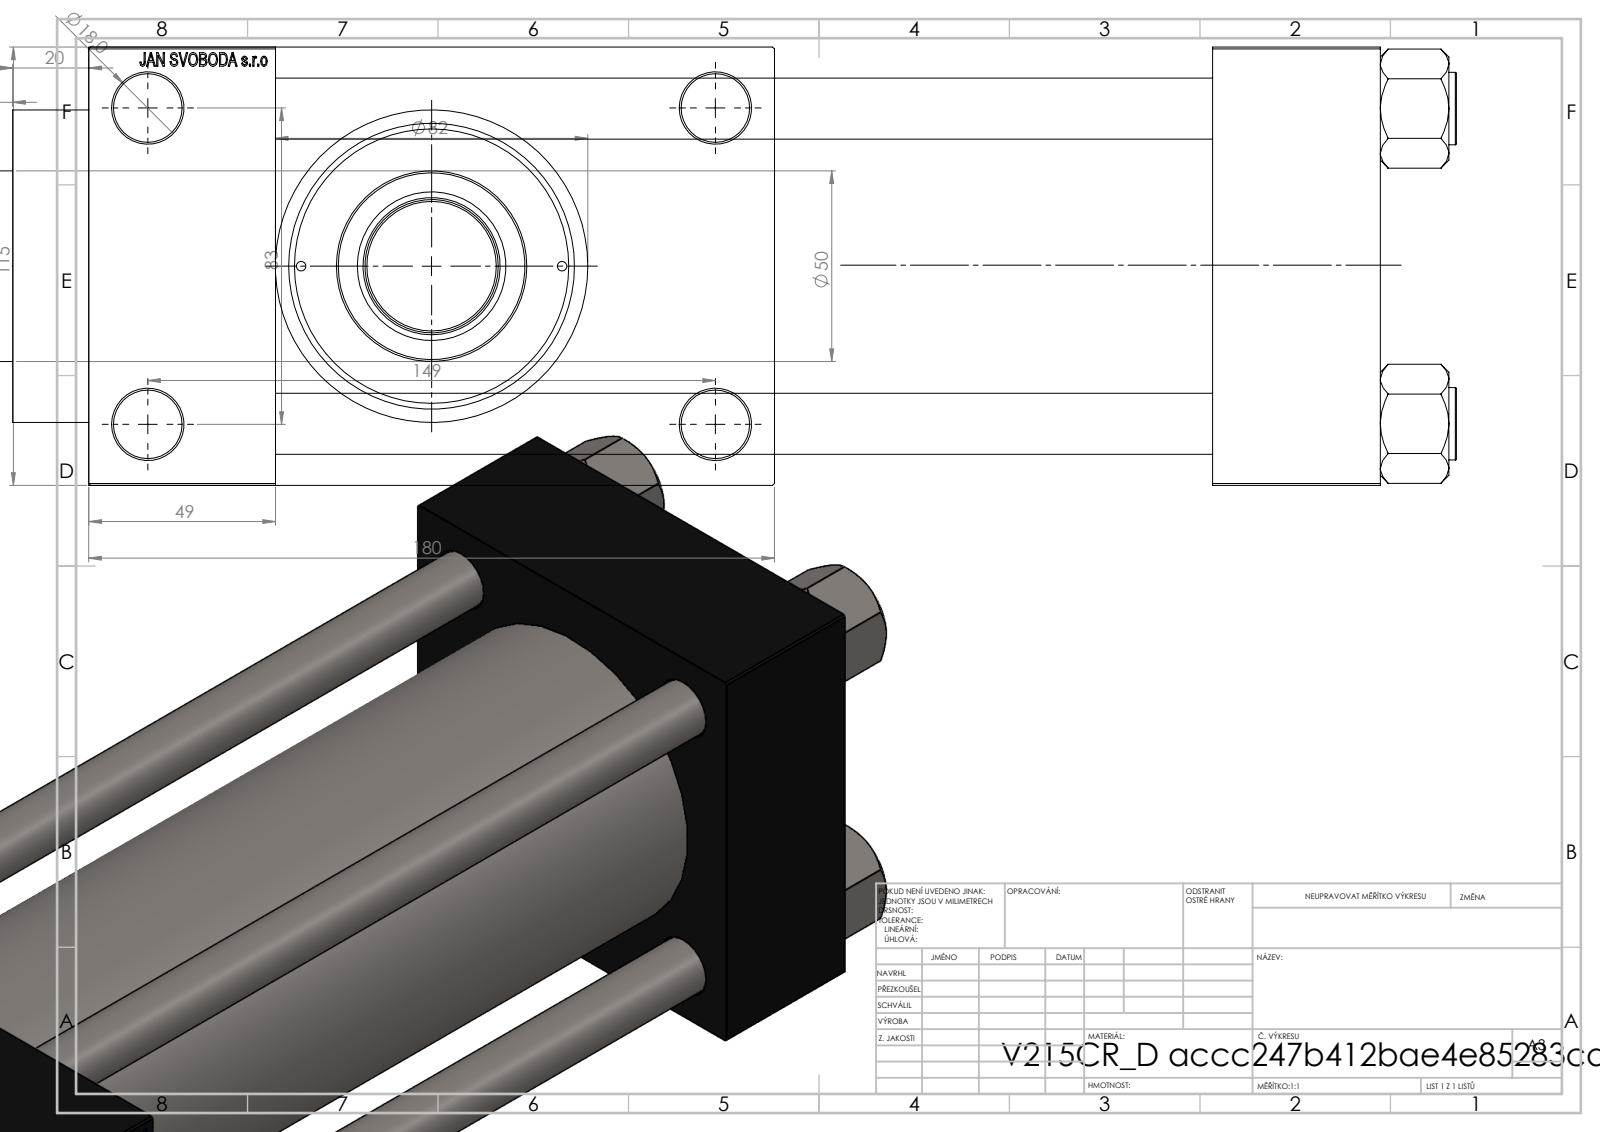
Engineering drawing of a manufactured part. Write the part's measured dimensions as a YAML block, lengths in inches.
part_name: "V215CR_VCP_D; V215CR_D_TYCINKA; V215CR_D_Body; NUT_M5_D (+2 more)"
step_written_by: "SolidWorks 2019 (CONFIG_CONTROL_DESIGN)"
units: inches
bodies: {solids: 12, faces: 1173, planar: 551, cylindrical: 96, other: 526}
overall_size: [17.559, 7.087, 4.528]
volume: 150.9
surface_area: 701.3
round_holes:
  - {diameter: 0.63, count: 4}
  - {diameter: 0.709, count: 4}
  - {diameter: 0.098, count: 2}
  - {diameter: 0.276, count: 2}
  - {diameter: 1.041, count: 2}
  - {diameter: 1.378, count: 2}
  - {diameter: 1.004, count: 1}
  - {diameter: 1.417, count: 1}
  - {diameter: 1.535, count: 1}
  - {diameter: 2.402, count: 1}
  - {diameter: 2.835, count: 1}
  - {diameter: 3.15, count: 1}
round_bosses_or_shafts:
  - {diameter: 0.748, count: 4}
  - {diameter: 3.386, count: 1}
  - {diameter: 3.228, count: 1}
  - {diameter: 1.969, count: 1}
  - {diameter: 1.378, count: 1}
  - {diameter: 0.827, count: 1}
face_to_face_distances: [4.528, 9.685, 1.929, 11.614, 1.732, 11.417, 13.346, 1.28, 5.807, 7.087]
hole_center_spacings: [1.305, 1.652, 2.276, 2.302, 3.256, 3.357, 3.393, 3.513]
